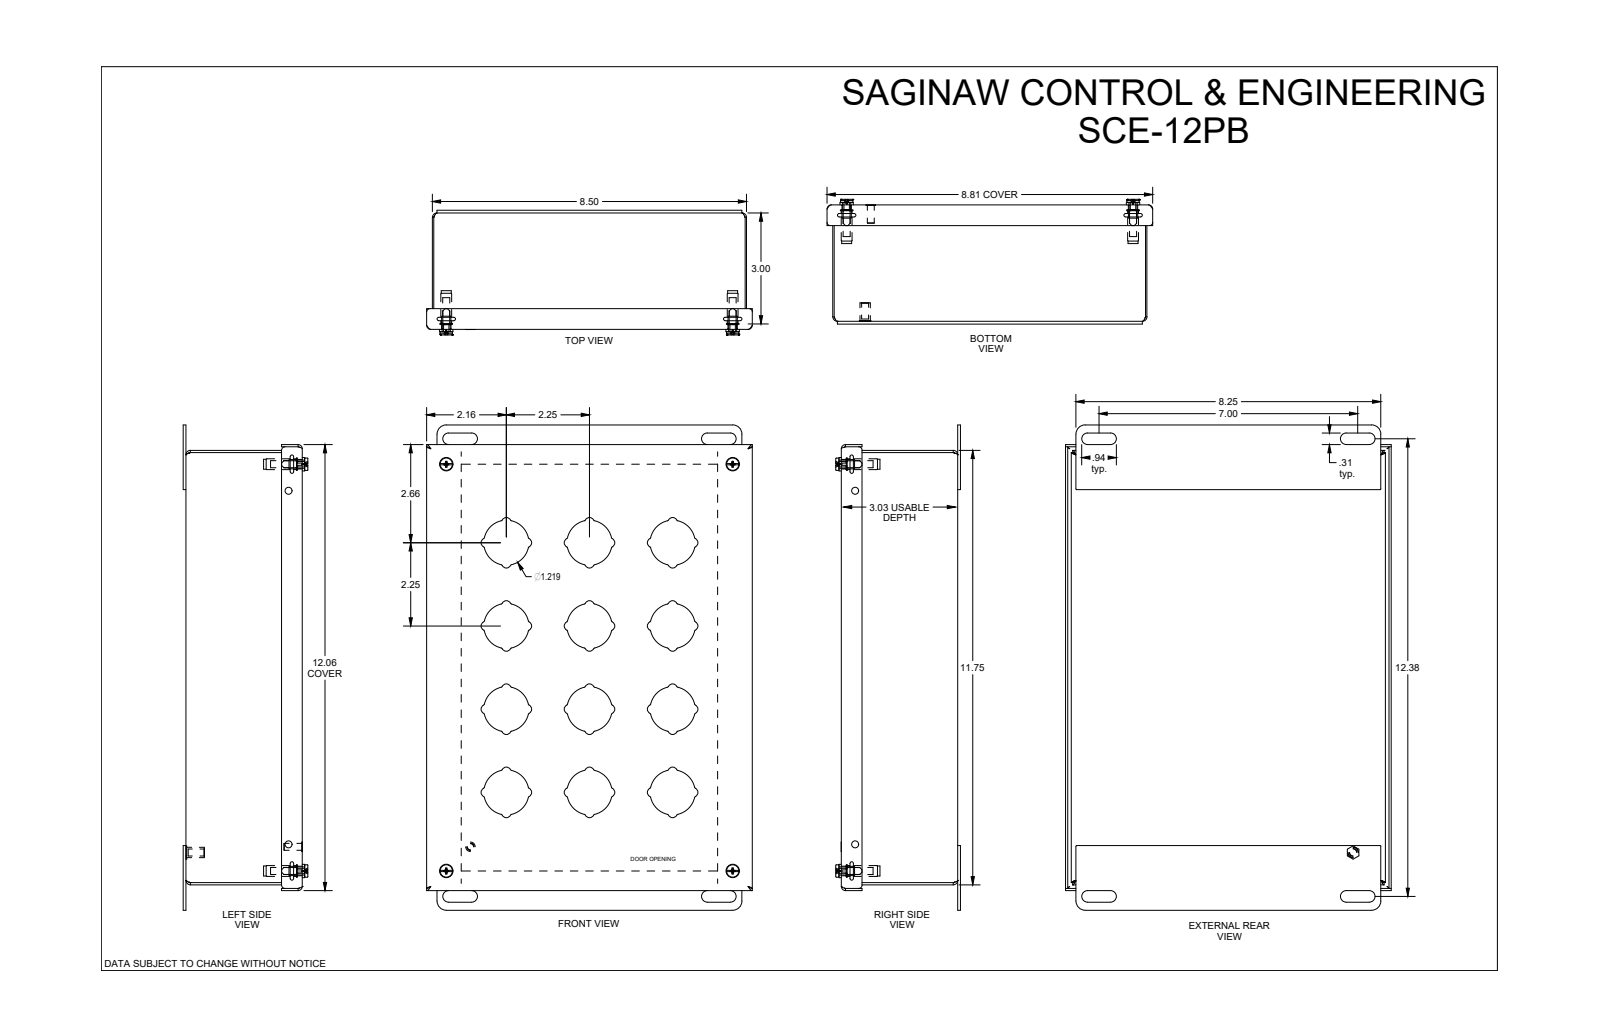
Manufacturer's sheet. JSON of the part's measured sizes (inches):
{"part_name": "SCE-12PB", "step_written_by": "SolidWorks 2019 (AUTOMOTIVE_DESIGN)", "units": "inches", "bodies": {"solids": 15, "faces": 612, "planar": 166, "cylindrical": 370, "other": 76}, "overall_size": [13.125, 8.813, 3.286], "volume_in3": 24.17, "surface_area_in2": 800.1, "round_holes": [[0.19, 5], [0.22, 4], [0.25, 4], [0.266, 4], [0.317, 4], [0.193, 1], [0.28, 1]], "round_bosses_or_shafts": [[0.437, 4], [0.362, 4], [0.34, 4], [0.292, 4], [0.27, 4], [0.26, 4], [0.28, 1], [0.256, 1]], "partial_cylinders_radius": [[0.04, 96], [0.125, 48], [0.06, 20], [0.609, 12], [0.015, 8], [0.115, 8], [0.156, 8], [0.245, 8]], "face_to_face_distances": [0.06, 3.088, 3.028, 3.148, 8.44, 11.69, 2.94, 0.148, 0.156, 8.5], "hole_center_spacings": [7.75, 11, 11, 13.46, 7.757, 7.757, 13.456, 0.619]}
